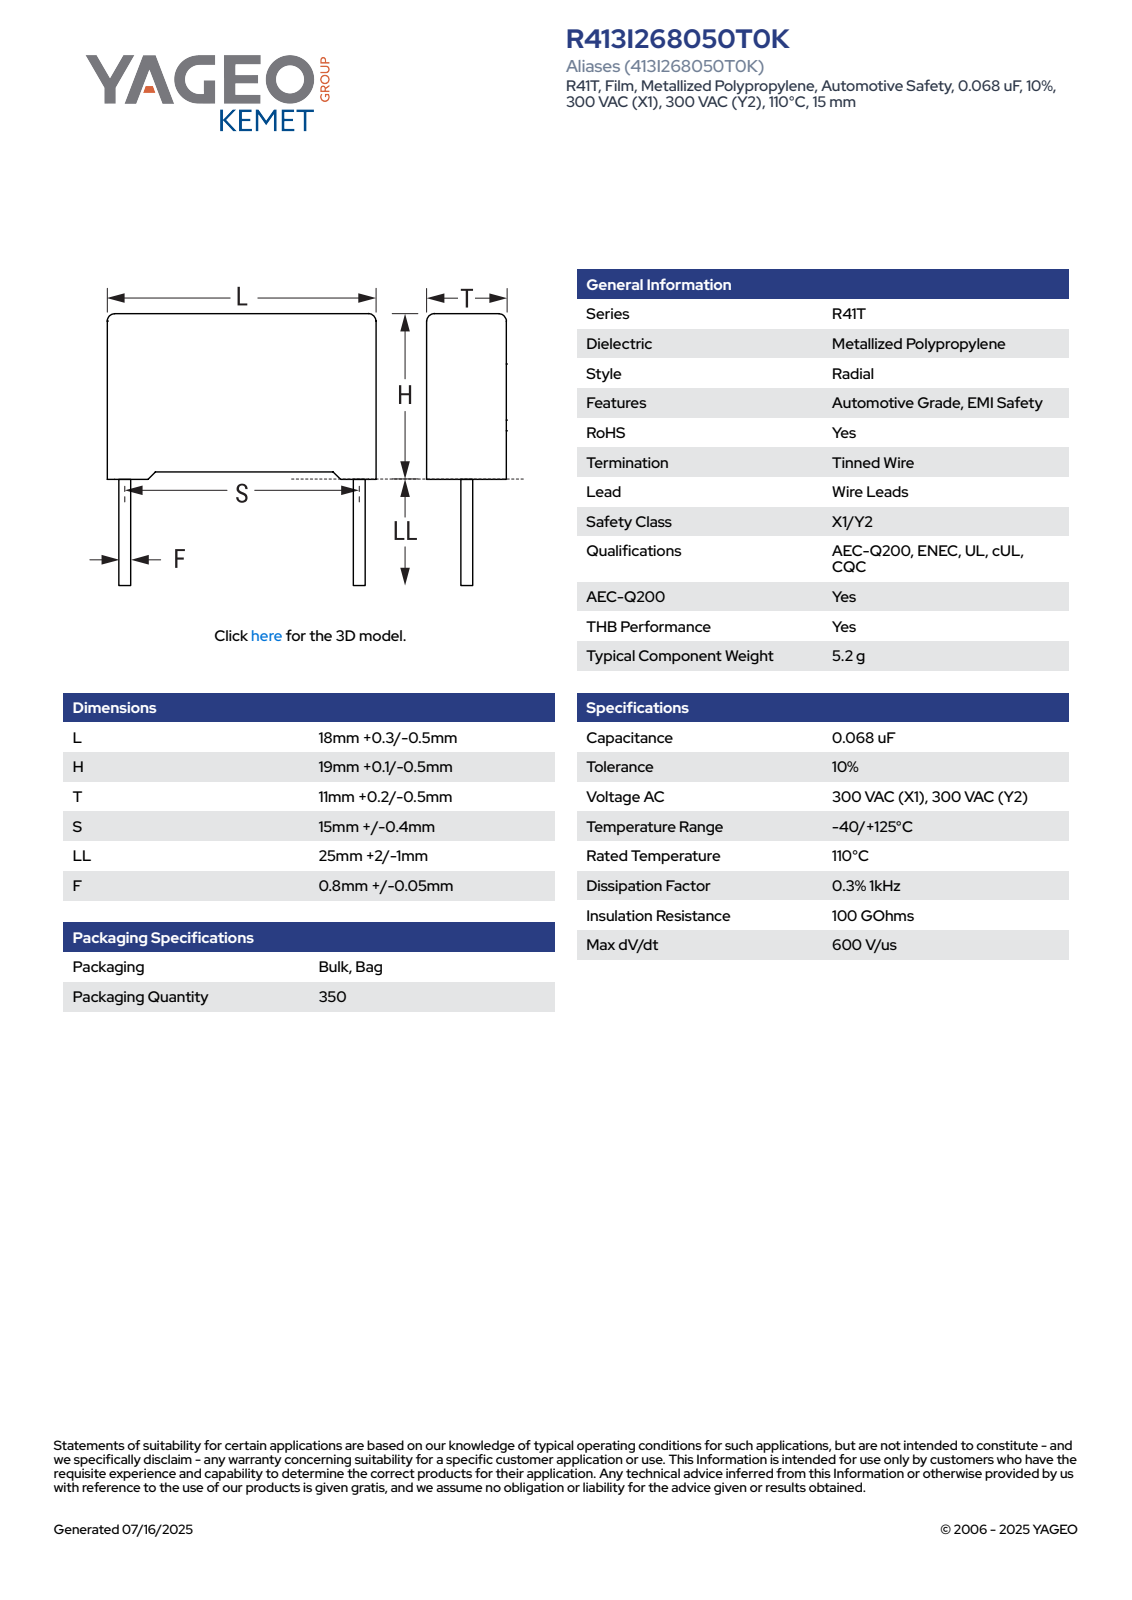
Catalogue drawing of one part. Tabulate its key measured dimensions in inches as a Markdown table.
| quantity | value |
| --- | --- |
| part name | CFR_RB2_18X19X11_L18.3H19.1T11.2S15LL27F0.85 |
| STEP written by | SolidWorks 2021 (AUTOMOTIVE_DESIGN) |
| units | inches |
| bodies | 4 solids, 85 faces (77 planar, 8 cylindrical, 0 other) |
| overall size | 1.815 × 0.72 × 0.441 |
| volume | 0.232 in³ |
| surface area | 2.649 in² |
| round bosses / shafts (diameter × count) | 0.033 × 2 |
| partial cylindrical surfaces (radius × count) | 0.02 × 4 |
| main face-to-face distances | 0.441, 0.72, 0.722, 0.024, 0.03, 0.752, 0.696, 0.026, 0.726, 0.417 |
